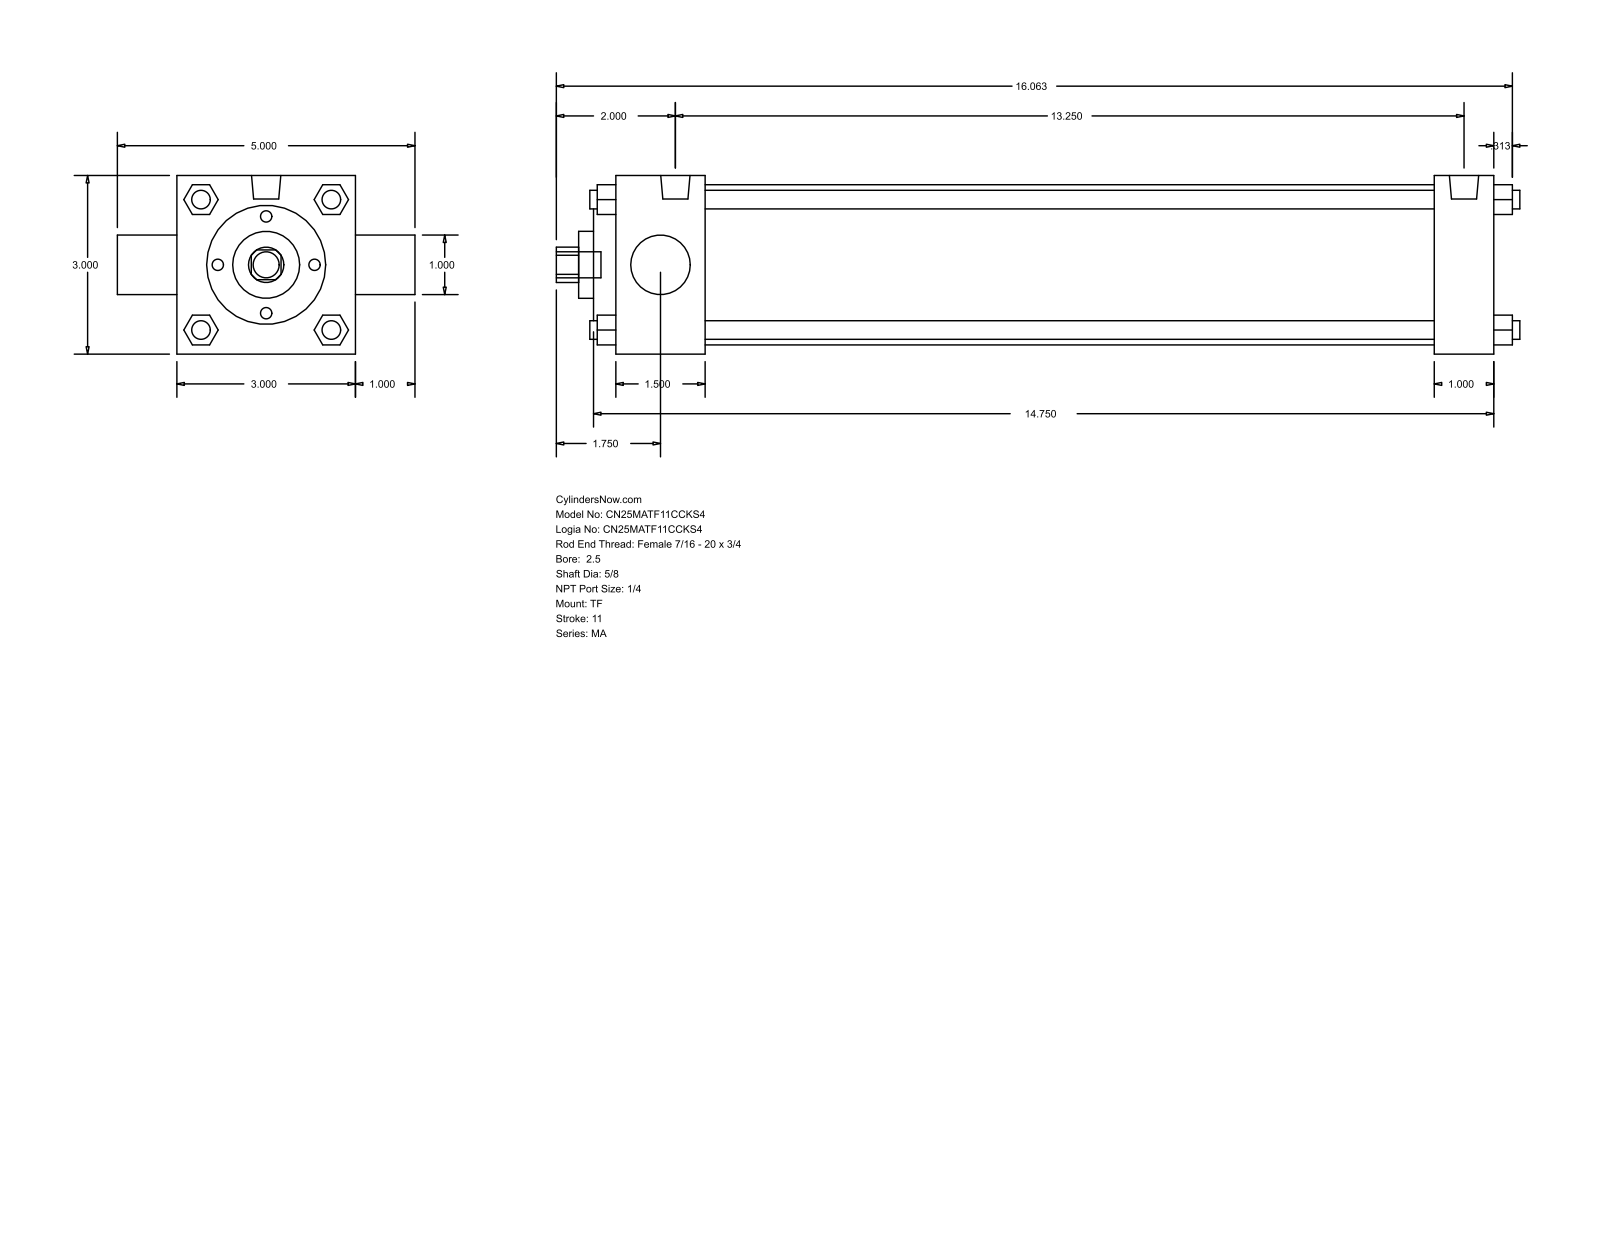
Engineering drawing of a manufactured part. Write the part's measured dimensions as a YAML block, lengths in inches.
part_name: "MA_TF__0250_0.625"
step_written_by: "GSSL Pune (CONFIG_CONTROL_DESIGN)"
units: inches
bodies: {solids: 0, faces: 122, planar: 93, cylindrical: 29, other: 0}
overall_size: [16.187, 5, 3]
round_holes:
  - {diameter: 0.625, count: 1}
  - {diameter: 1, count: 1}
  - {diameter: 1.125, count: 1}
  - {diameter: 2, count: 1}
  - {diameter: 2.69, count: 1}
round_bosses_or_shafts:
  - {diameter: 0.313, count: 7}
  - {diameter: 0.492, count: 2}
  - {diameter: 0.437, count: 1}
partial_cylinders:
  - {radius: 0.297, count: 1}
face_to_face_distances: [3, 14.75, 1, 1.5, 13.75, 12.25, 13.25, 0.5, 0.375, 1.875]
